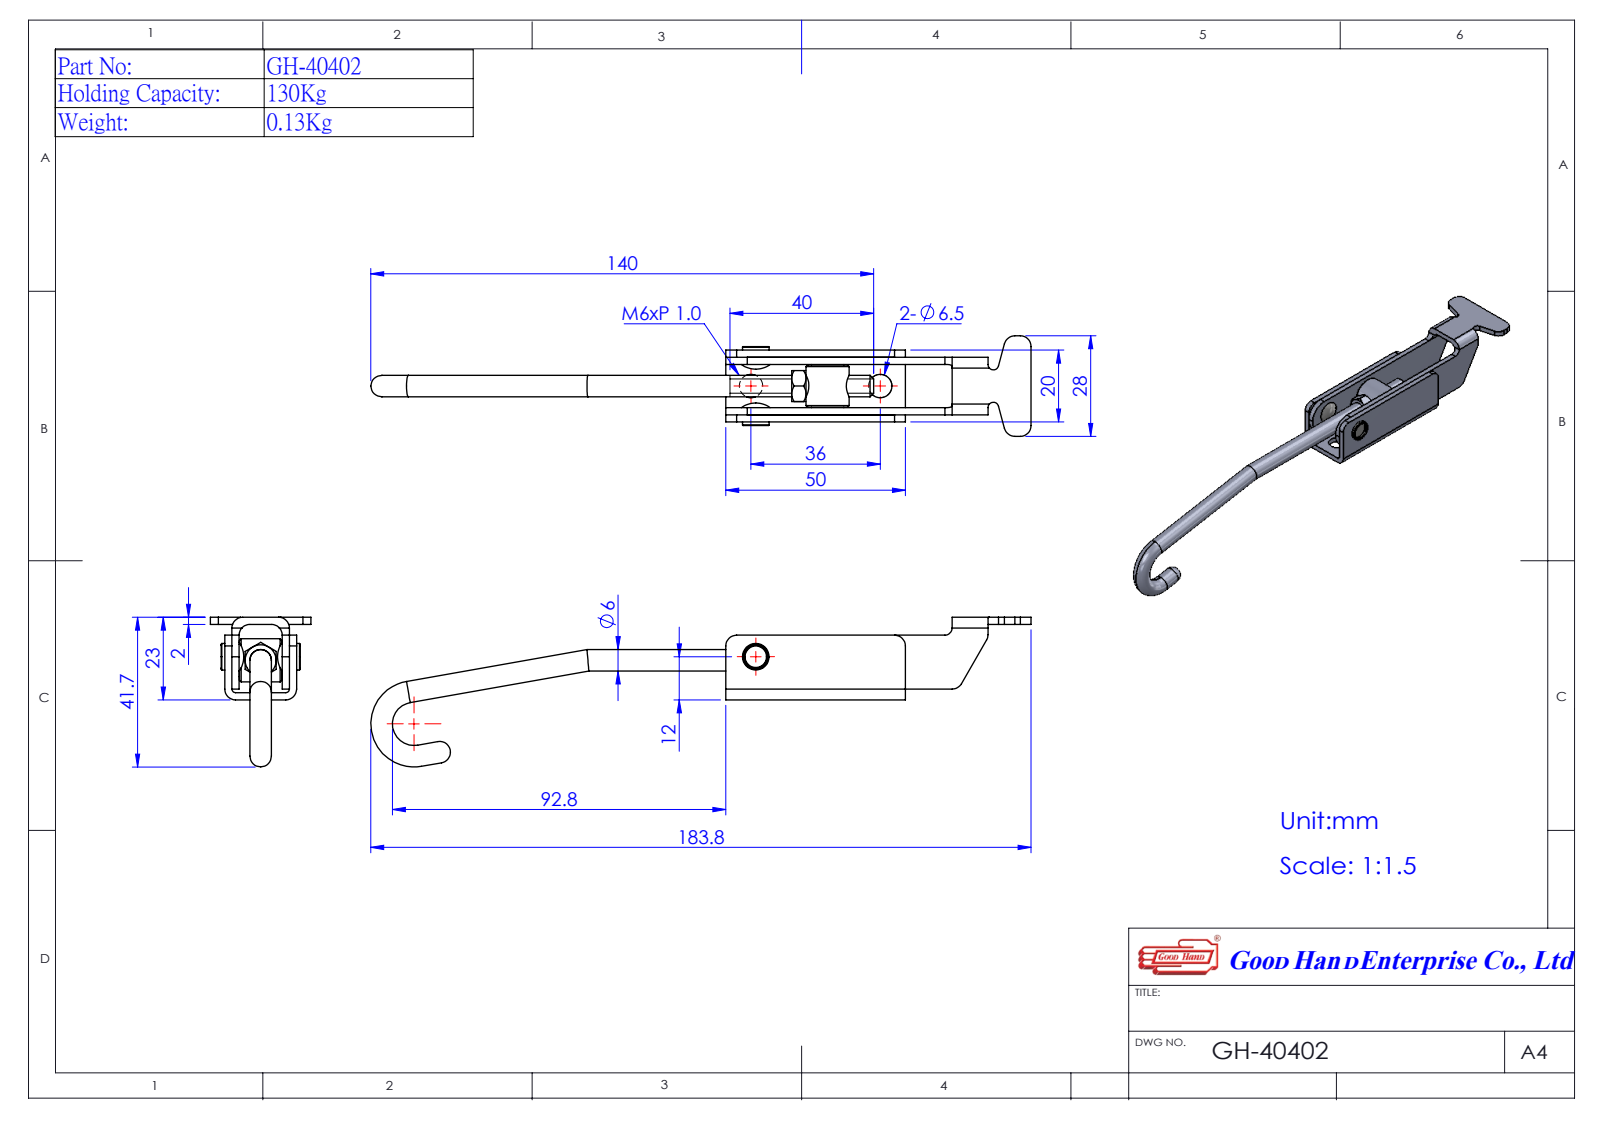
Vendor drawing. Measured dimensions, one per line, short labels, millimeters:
name: 14040213-1^GH-40402(簡化); 14040247-1^GH-40402(簡化); GH-40402(簡化); Group1^GH-40402(簡化) (+1 more)
written by: SolidWorks 2016 (AUTOMOTIVE_DESIGN)
unit: mm
bodies: 5 solids, 127 faces (48 planar, 58 cylindrical, 21 other)
size: 183.84 × 41.68 × 28
volume: 16 018 mm³; area: 15 744 mm²
holes: 2× ⌀6.5, 1× ⌀5, 1× ⌀6, 1× ⌀8
bosses: 2× ⌀6, 1× ⌀12, 1× ⌀7.4
rounds: 8× R3, 2× R1.5, 1× R2, 1× R6, 1× R9
face distances: 2, 16, 18, 14, 4, 20, 12, 21, 3, 5
hole spacings: 20.02, 36
